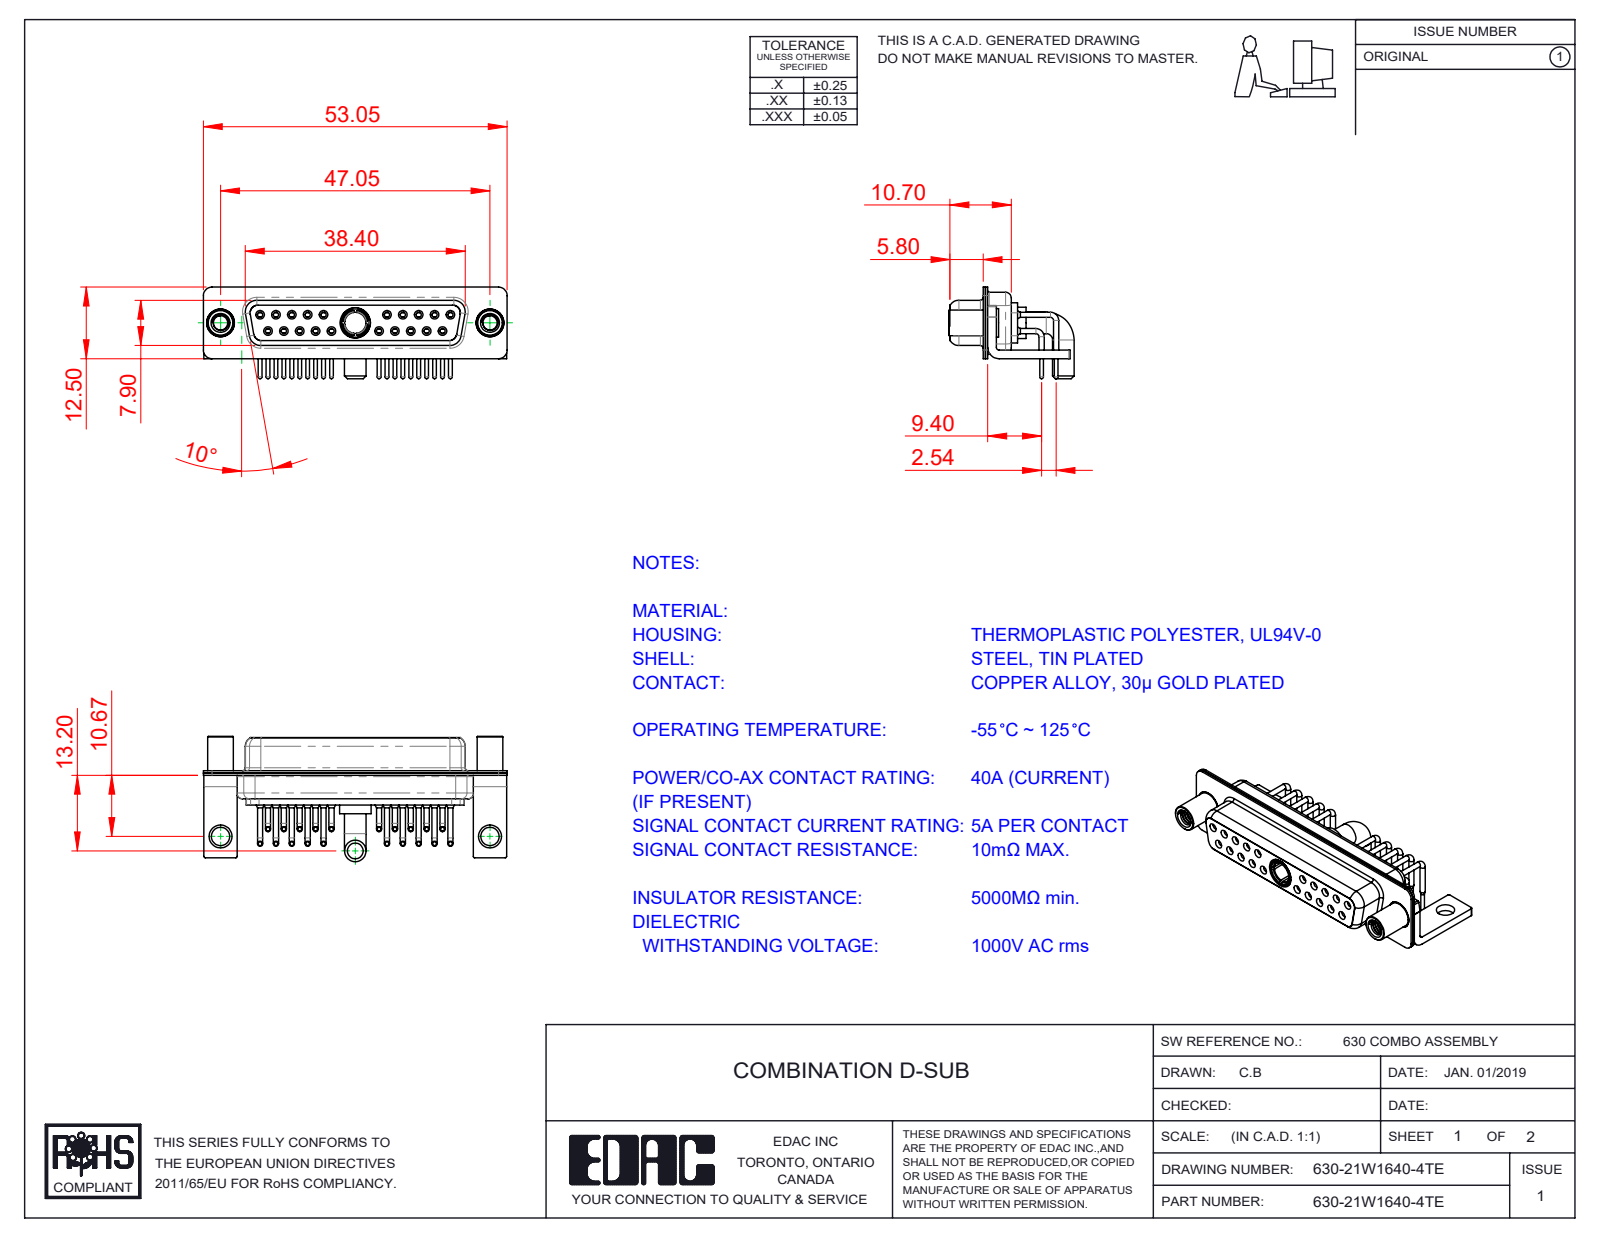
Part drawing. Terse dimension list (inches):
name: 630Combo Threaded Standoff_D; 630Combo Shell Front_25 Contacts; 630Combo Shell Rear_25 Contacts; 630Combo Stabilizer Bracket (+5 more)
written by: SolidWorks 2020 (CONFIG_CONTROL_DESIGN)
unit: in
bodies: 29 solids, 1515 faces (418 planar, 694 cylindrical, 403 other)
size: 2.089 × 0.861 × 0.63
volume: 0.274 in³; area: 15.99 in²
holes: 20× ⌀0.035, 20× ⌀0.043, 20× ⌀0.059, 20× ⌀0.079, 10× ⌀0.063, 10× ⌀0.067, 3× ⌀0.191, 2× ⌀0.098, 2× ⌀0.126, 2× ⌀0.157, 2× ⌀0.159, 1× ⌀0.146
bosses: 20× ⌀0.035, 20× ⌀0.026, 10× ⌀0.063, 2× ⌀0.197, 2× ⌀0.195, 2× ⌀0.189, 2× ⌀0.177, 2× ⌀0.148
rounds: 16× R0.01, 16× R0.059, 13× R0.079, 8× R0.053, 8× R0.063, 5× R0.02, 4× R0.024, 4× R0.026
face distances: 0.016, 0.018, 0.055, 0.333, 0.031, 0.071, 0.35, 0.244, 0.278, 0.059
hole spacings: 0.124, 0.109, 0.218, 0.327, 0.198, 0.763, 0.826, 0.872
